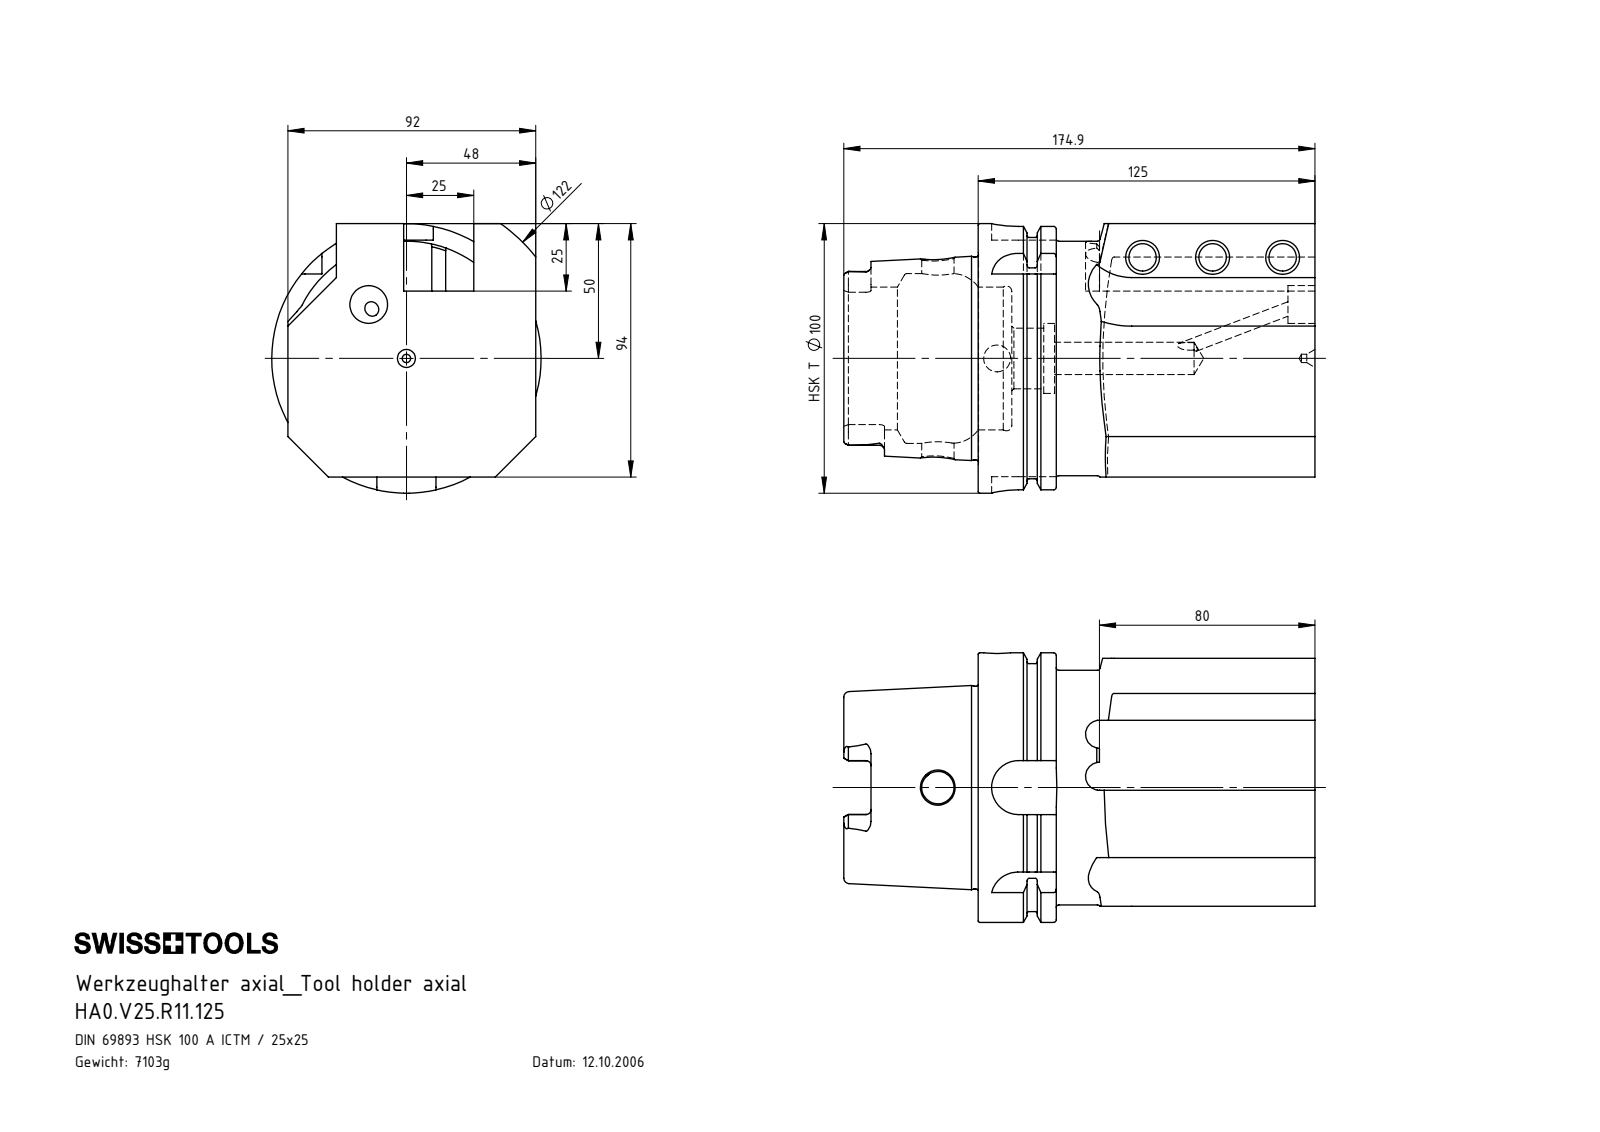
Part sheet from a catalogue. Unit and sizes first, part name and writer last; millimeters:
Units: millimetres
Overall size (bounding box): 177.71 × 100 × 100
Round holes (diameter × count): ⌀10.2 ×3, ⌀5 ×2, ⌀10 ×2, ⌀12 ×2, ⌀3.15 ×1, ⌀14 ×1, ⌀22.5 ×1, ⌀26 ×1, ⌀53 ×1, ⌀63 ×1
Round bosses / shafts (diameter × count): ⌀12 ×3, ⌀100 ×1, ⌀91.95 ×1, ⌀87 ×1, ⌀75.26 ×1
Partial cylindrical surfaces — rounded edges, fillets, slot ends (radius × count): R1.9 ×6, R4.88 ×4, R10 ×4, R5.2 ×2, R61 ×1
Main face-to-face distances: 69, 25, 92, 125, 94, 23, 26, 94.03, 49, 43
Hole centre spacings: 26, 24.41, 52, 65.74, 88.35, 112.44
Volume: 913 766 mm³ · Surface area: 97 672 mm²
Bodies: 6 solids, 199 faces (82 planar, 47 cylindrical, 70 other)
Part name (STEP PRODUCT): HA0.V25.R11.125; KU1-U14.001.012; KU1-U14.001.012_2; KU1-U14.001.012_1 (+2 more)
STEP written by: SolidWorks 2017 (AUTOMOTIVE_DESIGN)
